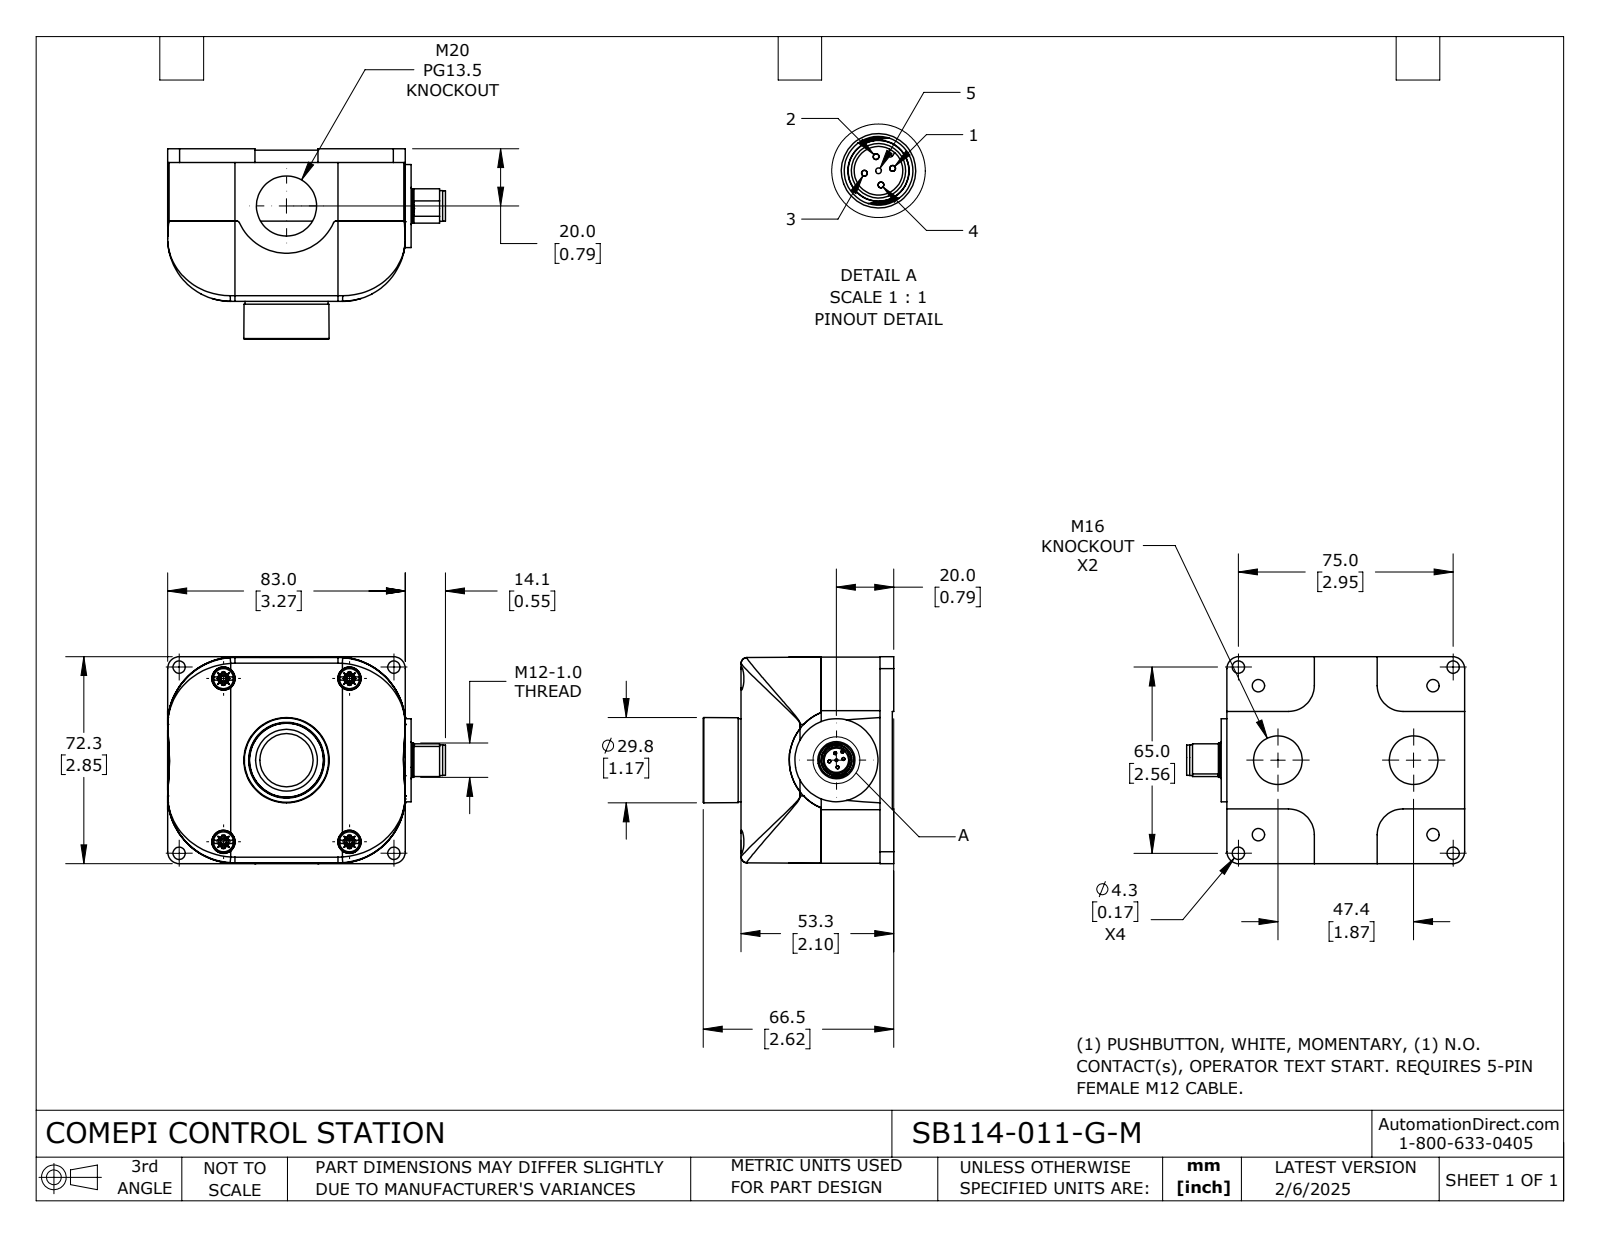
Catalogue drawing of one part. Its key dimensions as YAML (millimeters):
part_name: "SB114-011-G-M"
step_written_by: "SolidWorks 2024 (CONFIG_CONTROL_DESIGN)"
units: millimeters
bodies: {solids: 10, faces: 786, planar: 370, cylindrical: 273, other: 143}
overall_size: [97.1, 72.3, 66.5]
volume: 216800
surface_area: 61500
round_holes:
  - {diameter: 4.3, count: 8}
  - {diameter: 1, count: 4}
  - {diameter: 1.7, count: 4}
  - {diameter: 2.2, count: 4}
  - {diameter: 8.2, count: 4}
  - {diameter: 17, count: 2}
  - {diameter: 21, count: 2}
  - {diameter: 8.5, count: 1}
  - {diameter: 13.5, count: 1}
  - {diameter: 18.1, count: 1}
  - {diameter: 21.7, count: 1}
round_bosses_or_shafts:
  - {diameter: 1, count: 5}
  - {diameter: 7, count: 4}
  - {diameter: 2.2, count: 4}
  - {diameter: 1.7, count: 4}
  - {diameter: 29, count: 2}
  - {diameter: 0.6, count: 2}
  - {diameter: 26.4, count: 1}
  - {diameter: 25.8, count: 1}
partial_cylinders:
  - {radius: 0.5, count: 5}
  - {radius: 0.9, count: 4}
  - {radius: 2, count: 4}
  - {radius: 9, count: 4}
  - {radius: 9.7, count: 4}
  - {radius: 23.5, count: 4}
  - {radius: 0.2, count: 2}
  - {radius: 0.3, count: 2}
face_to_face_distances: [24.8, 2.5, 22.3, 52.8, 50.3, 28, 3, 53.3, 0.5, 25.3]
hole_center_spacings: [9.6, 26.9, 35.3, 40.1, 49.6, 58.9, 60.1, 68.3]
